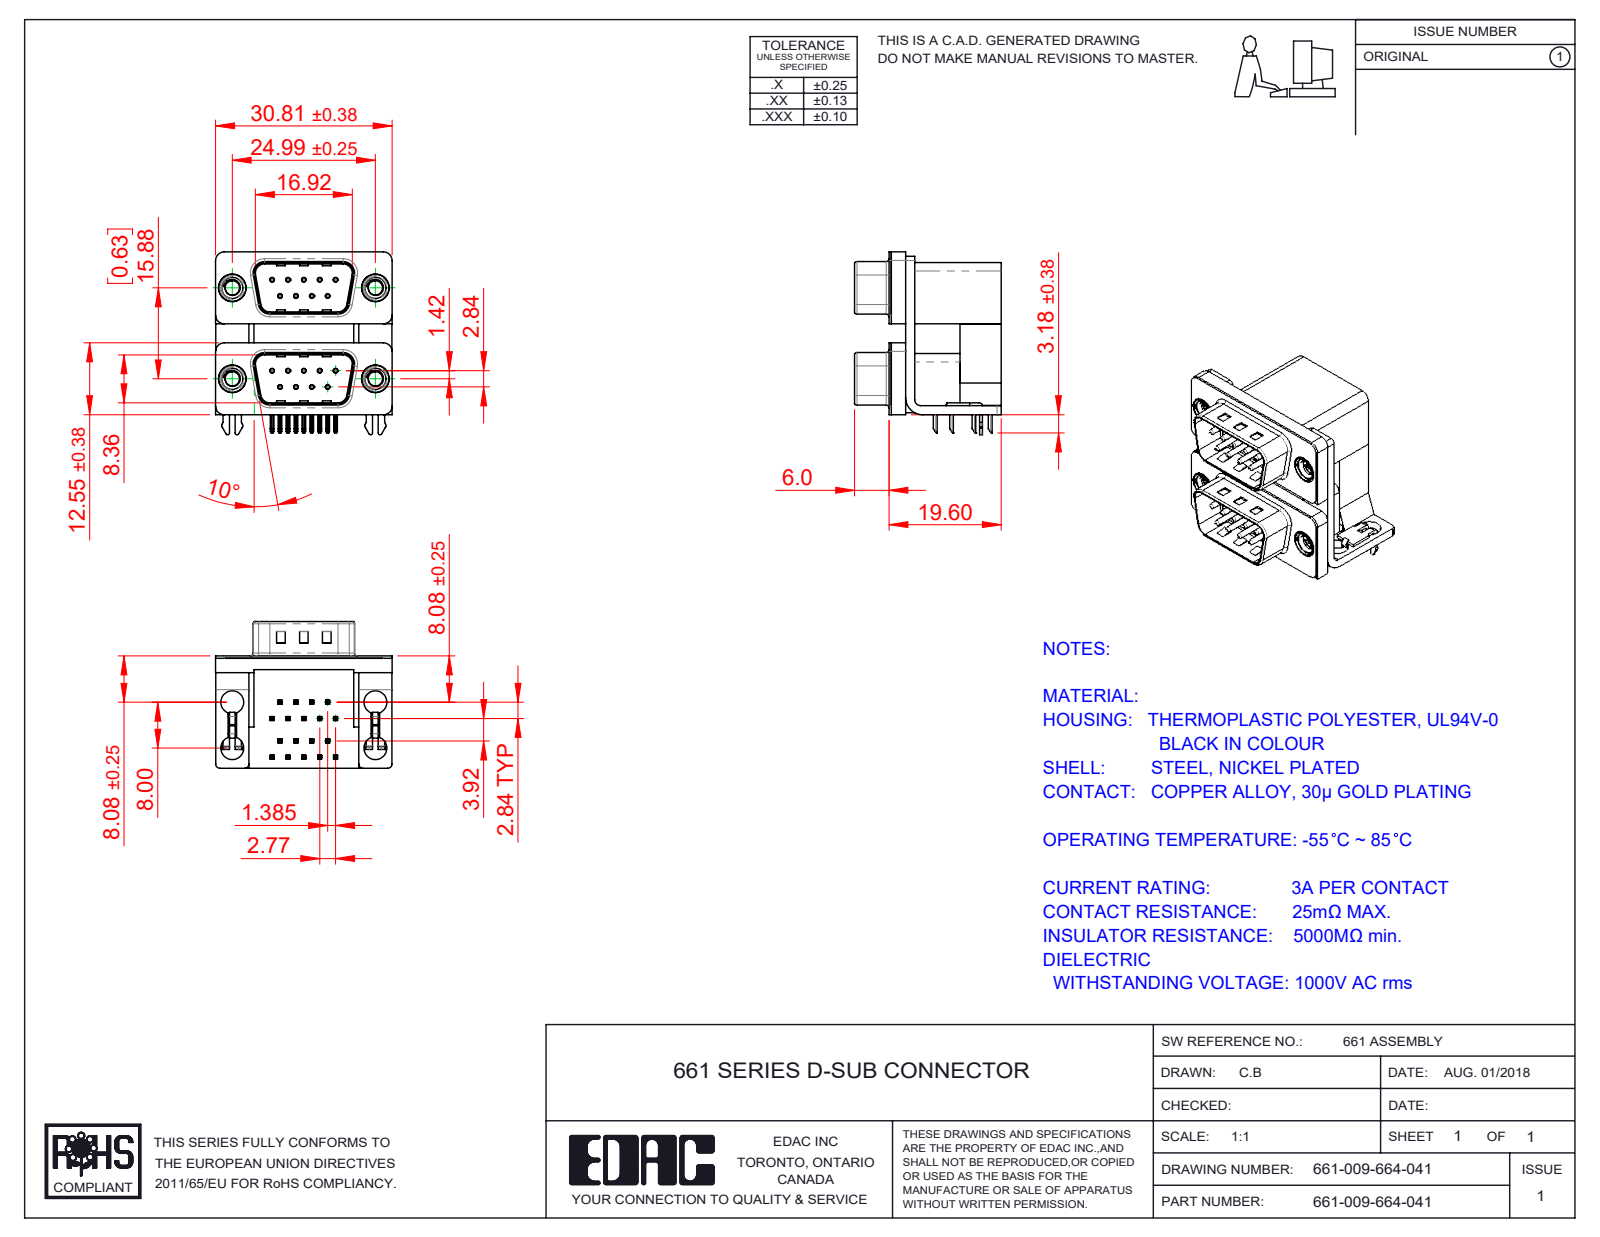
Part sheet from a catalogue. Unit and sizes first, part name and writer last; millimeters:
Units: millimetres
Overall size (bounding box): 31.93 × 30.81 × 25.6
Round holes (diameter × count): ⌀0.35 ×18, ⌀0.8 ×18, ⌀4 ×8, ⌀2.5 ×4, ⌀3.5 ×4, ⌀4.8 ×4, ⌀5 ×4
Round bosses / shafts (diameter × count): ⌀0.75 ×18, ⌀4.9 ×4, ⌀4.75 ×4, ⌀3.9 ×4
Partial cylindrical surfaces — rounded edges, fillets, slot ends (radius × count): R0.25 ×78, R0.12 ×36, R0.5 ×20, R1.5 ×13, R0.75 ×10, R0.9 ×8, R1.6 ×8, R2 ×8
Main face-to-face distances: 0.4, 2.5, 16.7, 19.2, 15.87, 7.2, 9.5, 12, 1.6, 19.6
Hole centre spacings: 3.16, 16.12, 2.77, 15.88, 16.82, 18.77, 5.54, 5.04
Volume: 9 817 mm³ · Surface area: 11 568 mm²
Bodies: 31 solids, 2060 faces (1230 planar, 632 cylindrical, 198 other)
Part name (STEP PRODUCT): 661 Contact Top Lower; 661-009-664-041; 661 Contact Bottom Upper_L; 661 Housing Spacer_09 Contacts L (+8 more)
STEP written by: SolidWorks 2020 (CONFIG_CONTROL_DESIGN)
